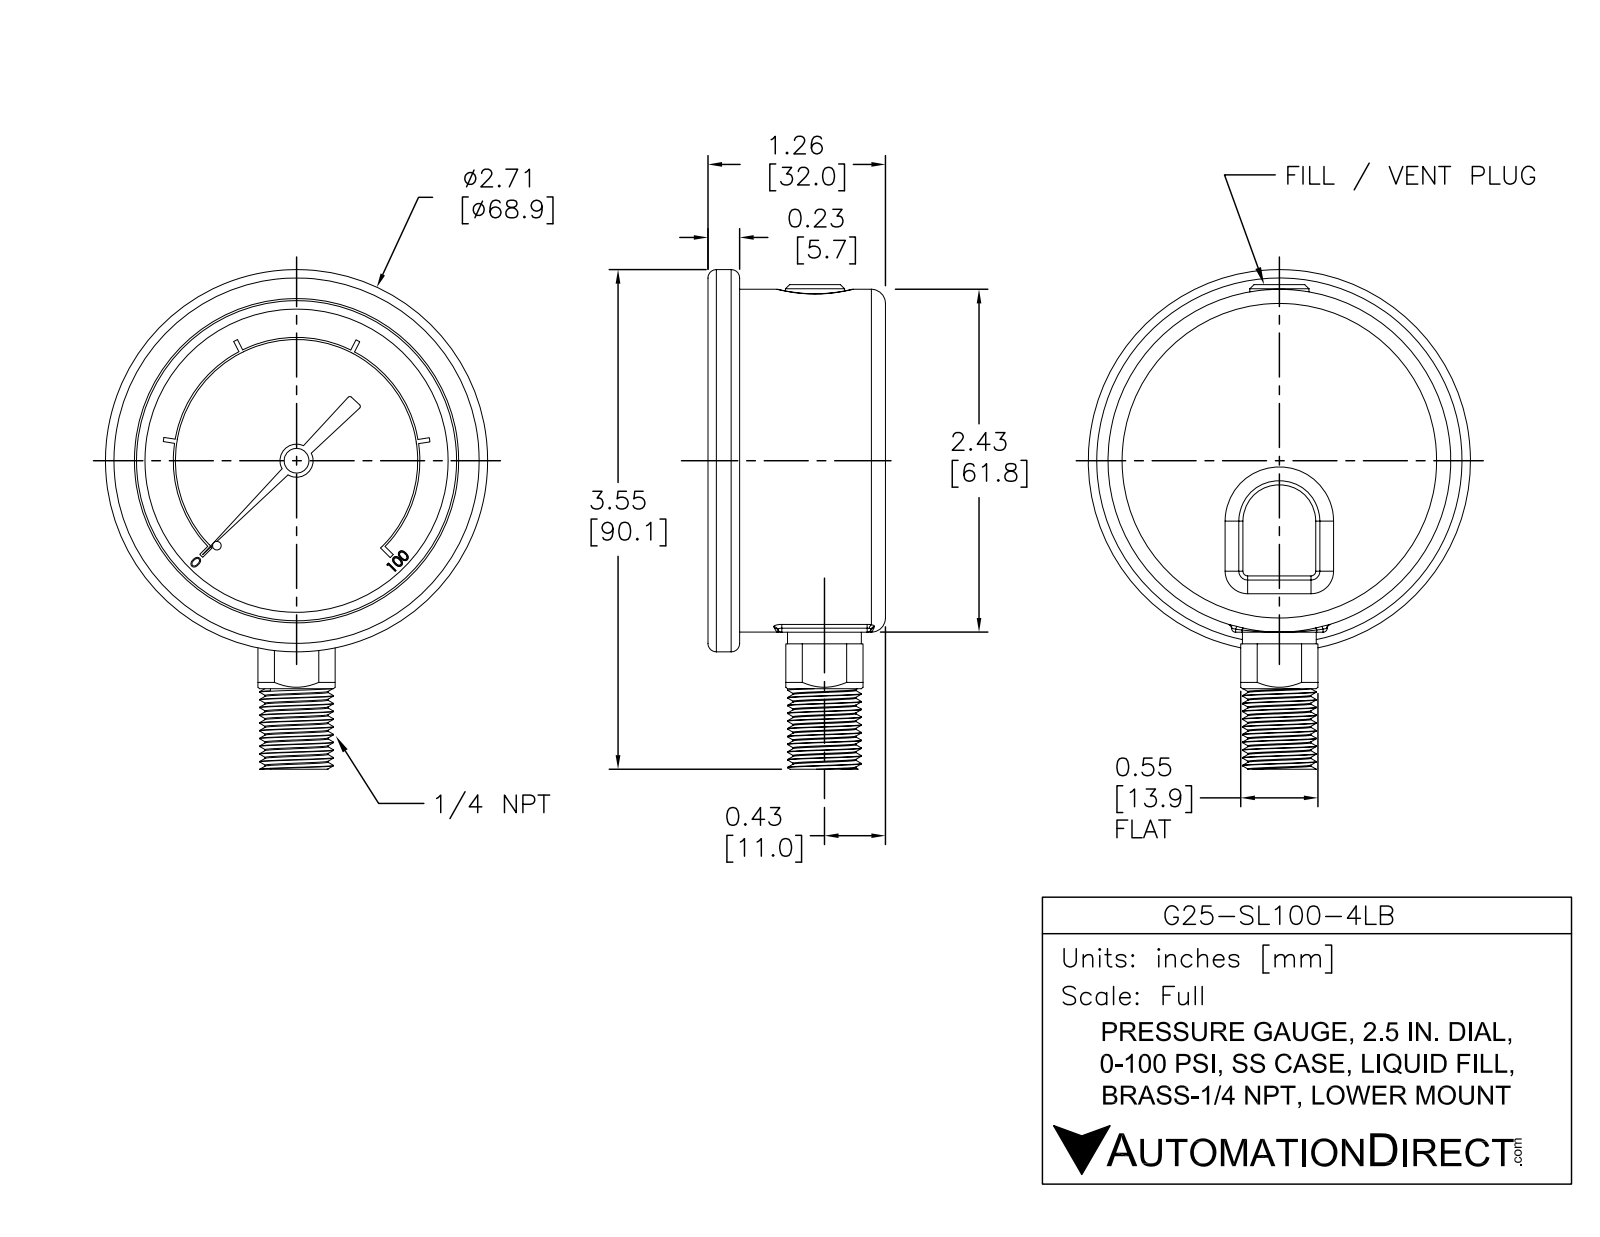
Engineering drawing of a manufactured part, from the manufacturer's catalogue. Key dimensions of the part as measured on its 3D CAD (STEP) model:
Part name (STEP PRODUCT): G25-SL100-4LB
STEP written by: SolidWorks 2021 (AUTOMOTIVE_DESIGN)
Units: inches
Bodies: 1 solid, 343 faces (195 planar, 85 cylindrical, 63 other)
Overall size (bounding box): 3.546 × 2.713 × 1.26
Volume: 5.273 in³ · Surface area: 24.68 in²
Round holes (diameter × count): ⌀0.027 ×1, ⌀0.071 ×1, ⌀0.119 ×1, ⌀2.272 ×1
Round bosses / shafts (diameter × count): ⌀2.713 ×1, ⌀2.433 ×1, ⌀0.524 ×1, ⌀0.42 ×1, ⌀0.235 ×1, ⌀0.176 ×1, ⌀0.14 ×1, ⌀0.041 ×1
Partial cylindrical surfaces — rounded edges, fillets, slot ends (radius × count): R0.03 ×9, R0.1 ×3, R0.015 ×2, R0.316 ×1, R0.86 ×1, R0.875 ×1
Main face-to-face distances: 1.01, 1.26, 0.25, 1.035, 0.025, 0.225, 0.1, 0.91, 0.935, 1.16
Hole centre spacings: 0.067
